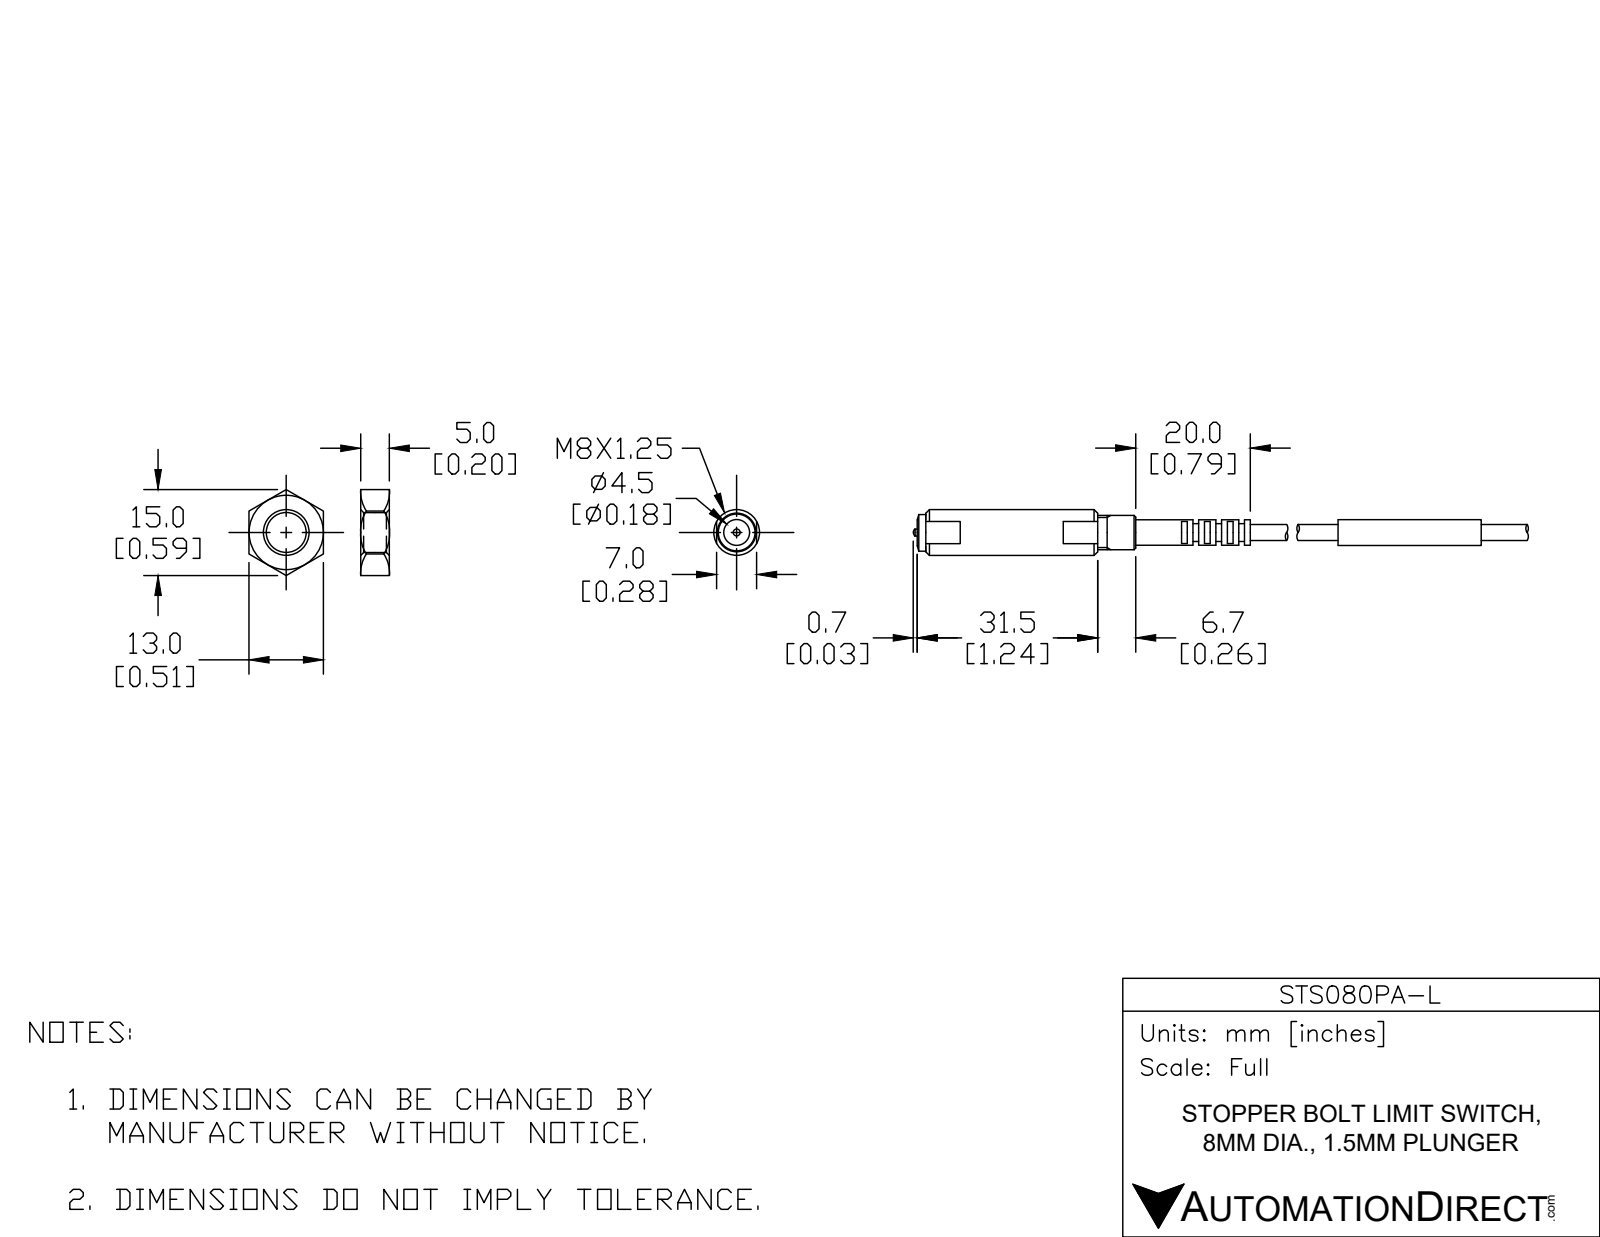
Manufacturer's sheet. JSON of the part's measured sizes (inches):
{"part_name": "STS080PA-L", "step_written_by": "SolidWorks 2017 (CONFIG_CONTROL_DESIGN)", "units": "inches", "bodies": {"solids": 2, "faces": 191, "planar": 81, "cylindrical": 88, "other": 22}, "overall_size": [4.325, 0.315, 0.315], "volume_in3": 0.138, "surface_area_in2": 3.582, "round_bosses_or_shafts": [[0.315, 1], [0.248, 1], [0.236, 1], [0.177, 1], [0.175, 1], [0.122, 1], [0.11, 1], [0.047, 1]], "face_to_face_distances": [0.039, 0.118, 0.079, 0.157, 0.276, 0.197, 0.236, 0.315, 0.354, 0.394]}
